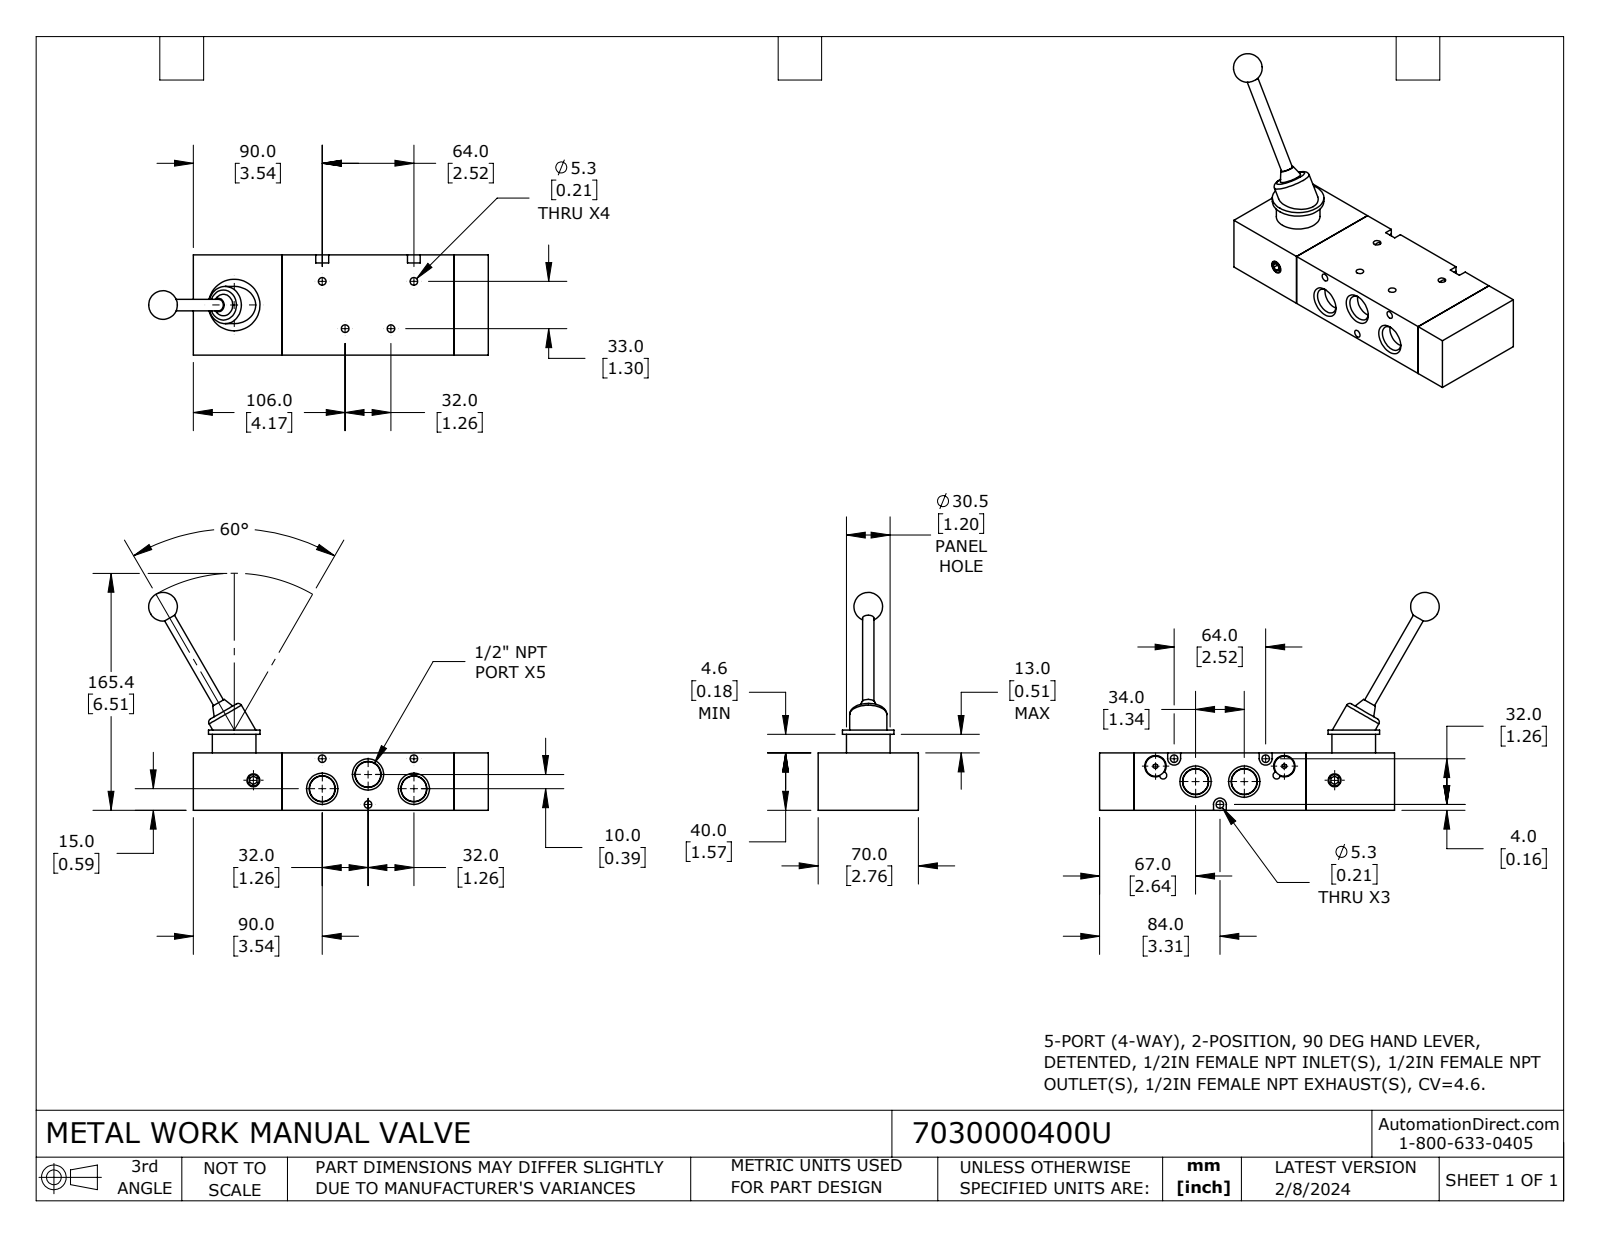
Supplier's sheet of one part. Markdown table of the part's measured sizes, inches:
| quantity | value |
| --- | --- |
| part name | 7030000400U |
| STEP written by | SolidWorks 2023 (CONFIG_CONTROL_DESIGN) |
| units | inches |
| bodies | 3 solids, 155 faces (72 planar, 57 cylindrical, 26 other) |
| overall size | 9.339 × 5.988 × 2.756 |
| volume | 35.65 in³ |
| surface area | 120.8 in² |
| round holes (diameter × count) | 0.209 × 7, 0.587 × 2, 0.354 × 1 |
| round bosses / shafts (diameter × count) | 0.551 × 2, 1.417 × 1, 1.201 × 1, 1.024 × 1, 0.315 × 1, 0.313 × 1 |
| partial cylindrical surfaces (radius × count) | 0.177 × 3, 0.098 × 2 |
| main face-to-face distances | 1.575, 2.756, 4.724, 0.945, 5.669, 8.11, 7.165, 2.441, 0.354, 2.402 |
| hole center spacings | 0.552, 1.444, 1.781, 2.061, 2.293, 2.52, 3.039, 1.26 |
